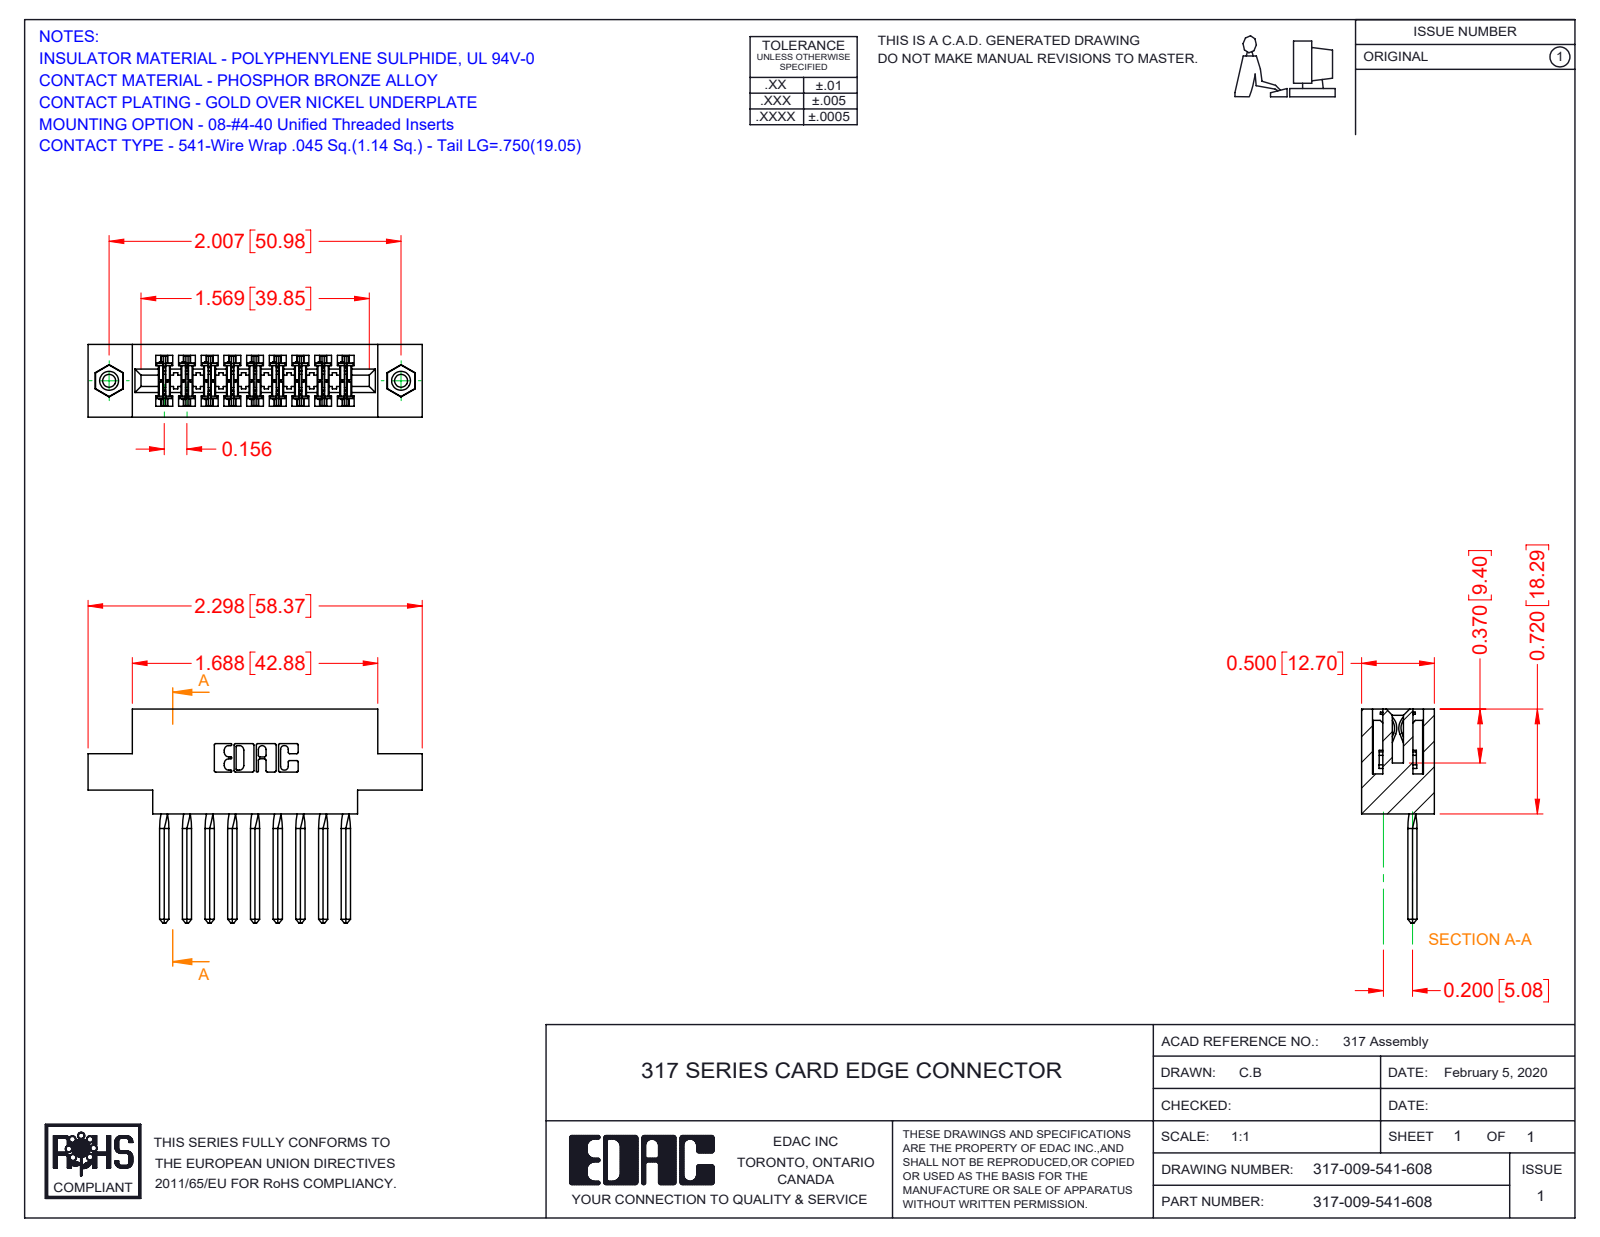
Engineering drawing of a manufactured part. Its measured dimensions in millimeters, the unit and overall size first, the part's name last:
Units: millimetres
Overall size (bounding box): 58.4 × 37.3 × 12.7
Round holes (diameter × count): ⌀2.3 ×2, ⌀3.2 ×2, ⌀4 ×2
Round bosses / shafts (diameter × count): ⌀3.9 ×2
Partial cylindrical surfaces — rounded edges, fillets, slot ends (radius × count): R0.3 ×22, R0.4 ×18, R0.2 ×6, R0.8 ×6, R0.7 ×3, R2.4 ×2, R2.5 ×2, R2.8 ×2
Main face-to-face distances: 12.7, 1.9, 10.8, 2.8, 1.7, 5.6, 4, 8.4, 8.9, 3.5
Hole centre spacings: 51
Volume: 8 440 mm³ · Surface area: 10 850 mm²
Bodies: 12 solids, 1530 faces (1206 planar, 272 cylindrical, 52 other)
Part name (STEP PRODUCT): 317-009-541-678; 317-290-002_541; 317 Part_.156 Dia - TI; 345-250-001_345-250-003-102
STEP written by: SolidWorks 2016 (CONFIG_CONTROL_DESIGN)
